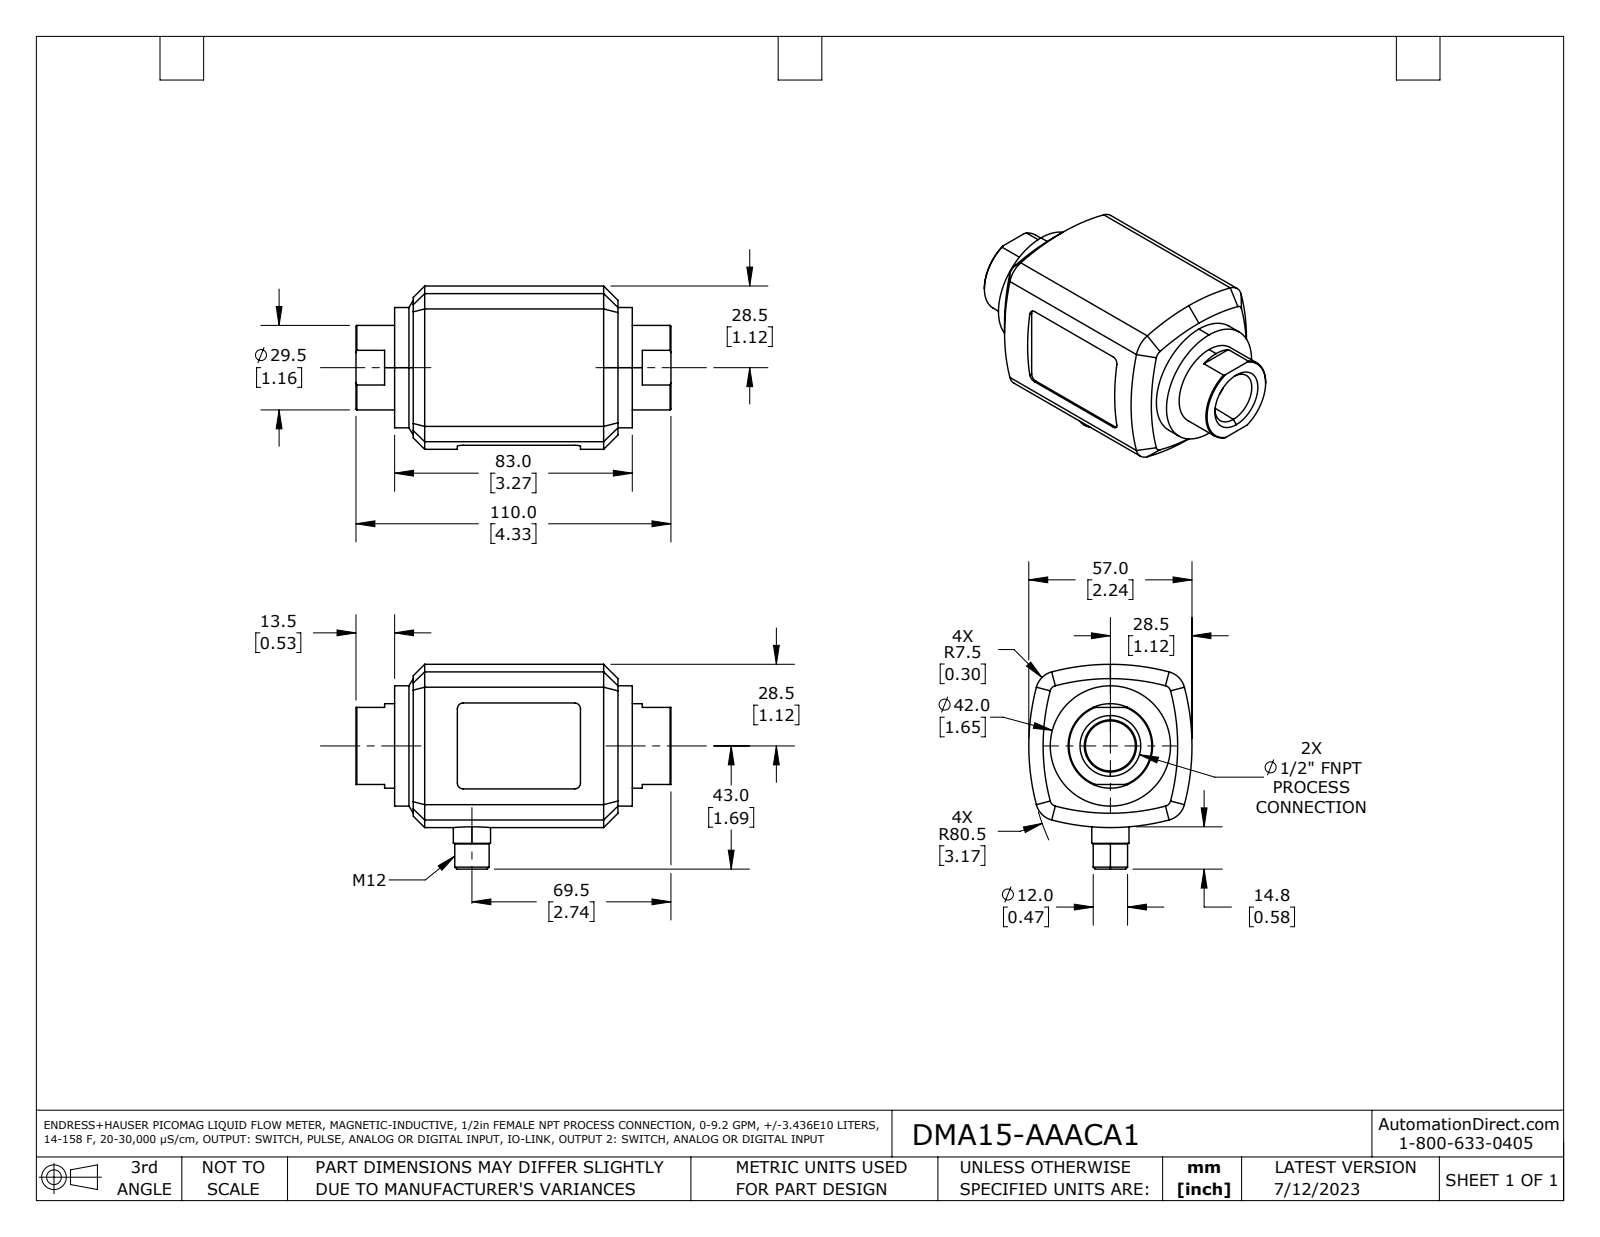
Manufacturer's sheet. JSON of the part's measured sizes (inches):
{"part_name": "DMA15-AAACA1", "step_written_by": "SolidWorks 2021 (AUTOMOTIVE_DESIGN)", "units": "inches", "bodies": {"solids": 1, "faces": 88, "planar": 25, "cylindrical": 29, "other": 34}, "overall_size": [4.331, 2.815, 2.244], "volume_in3": 14.15, "surface_area_in2": 38.82, "round_holes": [[0.382, 1]], "round_bosses_or_shafts": [[1.654, 1], [1.161, 1], [0.512, 1], [0.473, 1], [0.472, 1]], "partial_cylinders_radius": [[0.079, 4], [0.295, 4], [3.169, 4]], "face_to_face_distances": [3.268, 3.071, 0.197, 0.531, 3.799, 0.534, 3.796, 3.265, 0.256, 2.815]}
